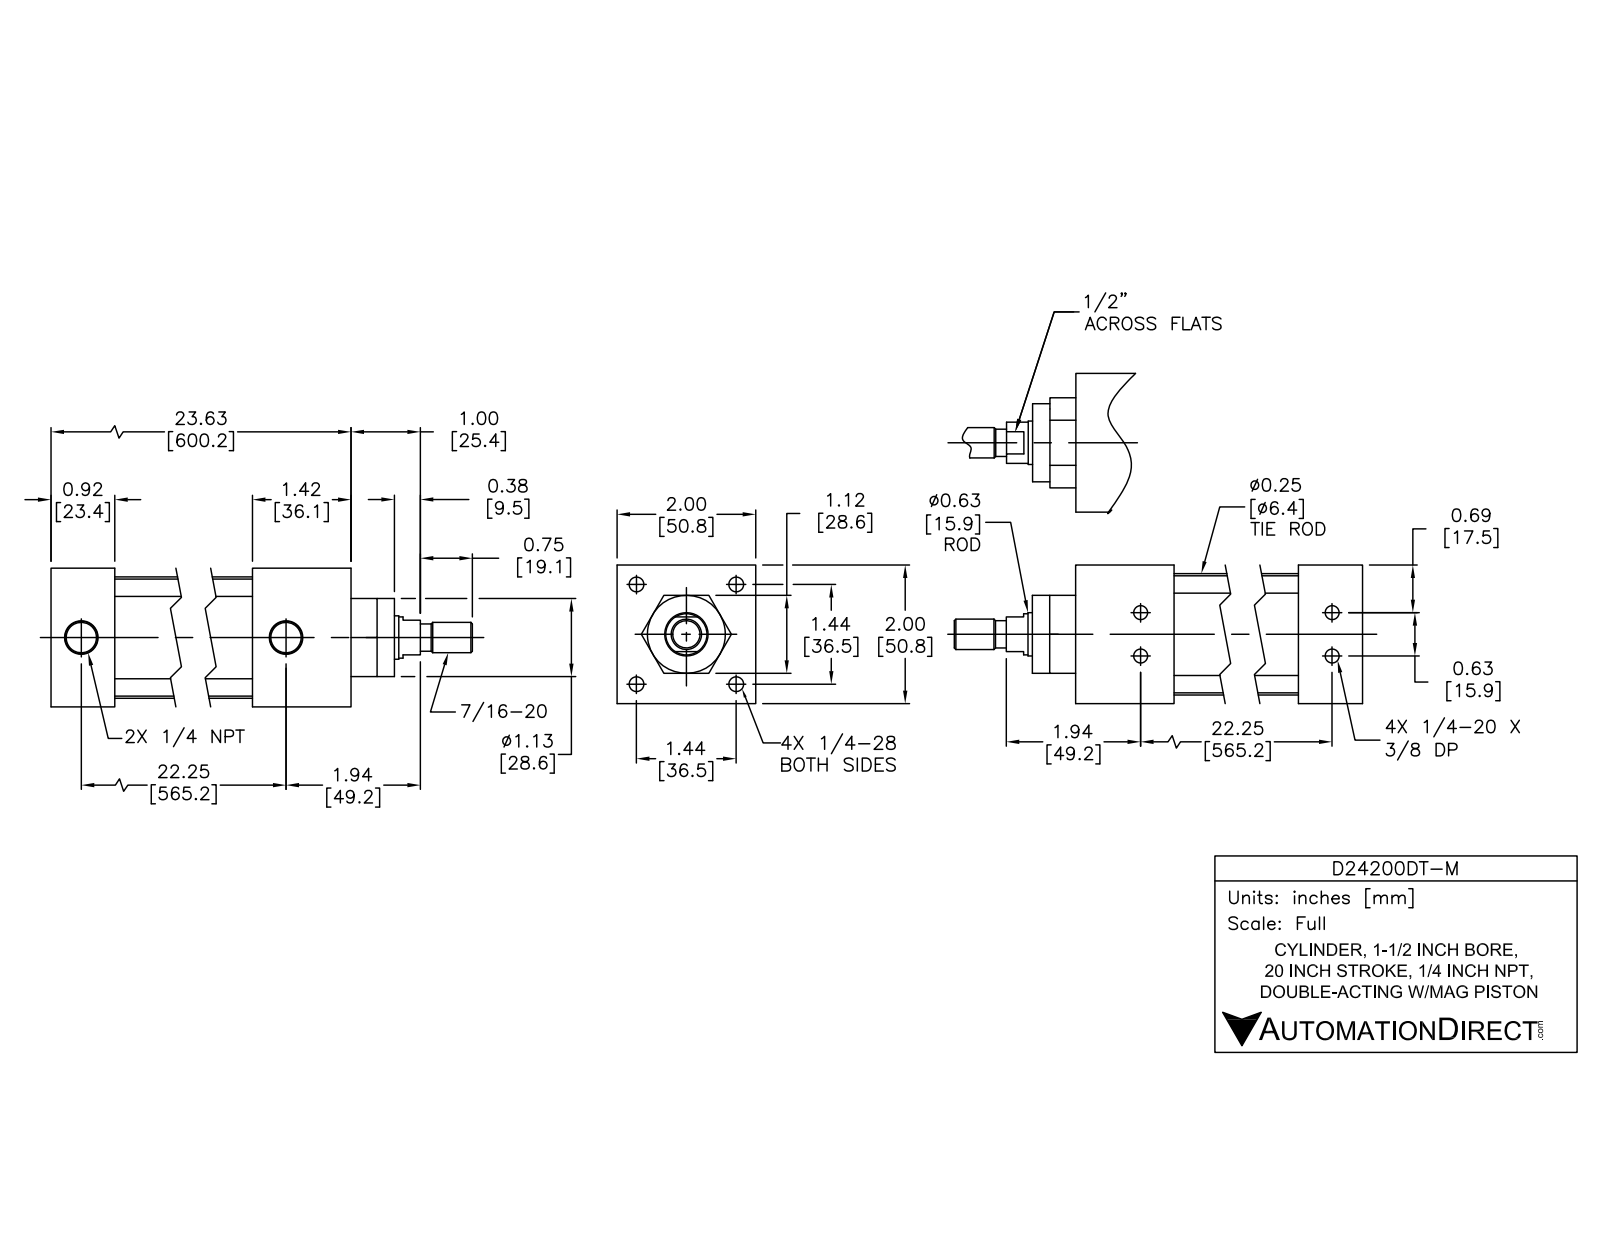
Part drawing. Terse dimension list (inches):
name: D24200DT-M PISTON; D24200DT-M; D24200DT-M BODY
written by: SolidWorks 2015 (AUTOMOTIVE_DESIGN)
unit: in
bodies: 12 solids, 303 faces (99 planar, 114 cylindrical, 90 other)
size: 25.371 × 2 × 2
volume: 34.63 in³; area: 392.1 in²
holes: 4× ⌀0.196, 4× ⌀0.211, 4× ⌀0.281, 4× ⌀0.406, 2× ⌀0.297, 2× ⌀0.477, 1× ⌀0.625, 1× ⌀0.628, 1× ⌀1.5
bosses: 4× ⌀0.39, 4× ⌀0.25, 4× ⌀0.222, 1× ⌀1.75, 1× ⌀1.497, 1× ⌀1.121, 1× ⌀0.622, 1× ⌀0.59
rounds: 4× R0.2
face distances: 2, 23.621, 1.42, 22.201, 22.701, 21.281, 0.92, 1.121, 22.601, 21.181
hole spacings: 0.313, 1.014, 1.434, 0.625, 2.028, 22.247, 22.248, 22.248
